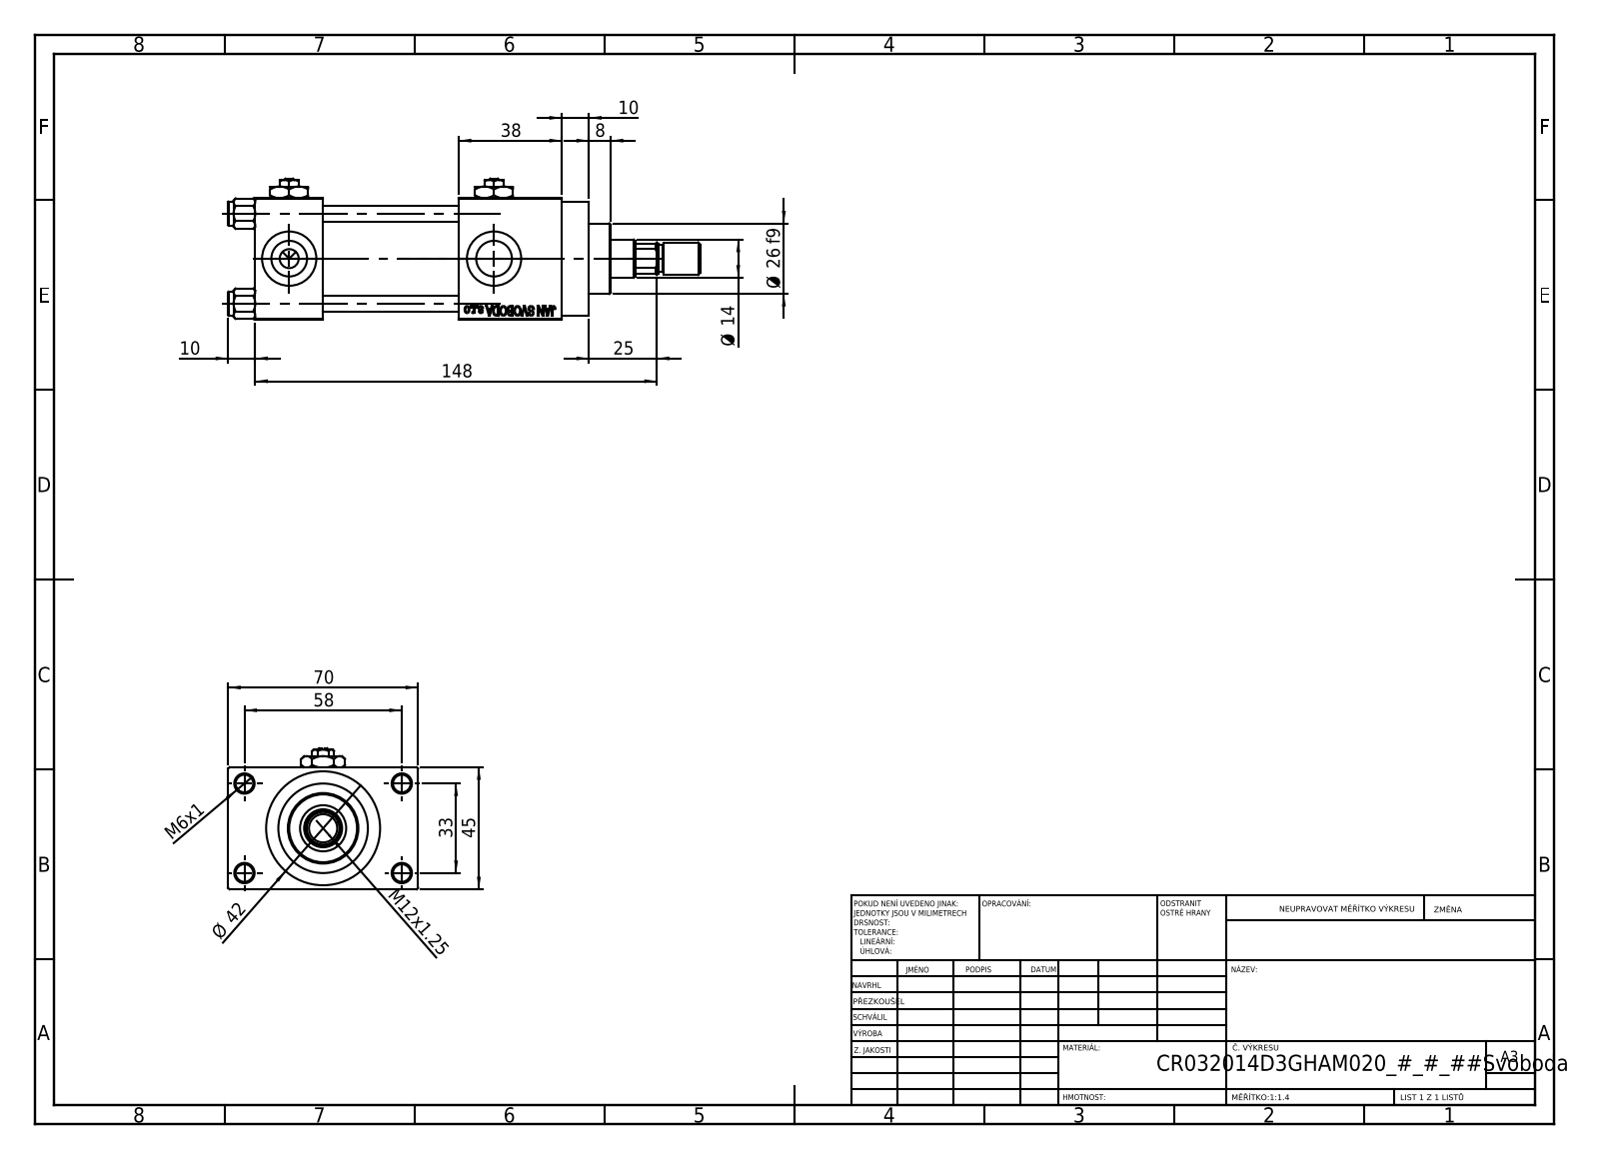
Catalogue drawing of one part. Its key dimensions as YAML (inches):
part_name: "ROD_END_AH; V215CR_D_Body; V215CR_D_TYCINKA; V215CR_VCP_D (+3 more)"
step_written_by: "SolidWorks 2019 (CONFIG_CONTROL_DESIGN)"
units: inches
bodies: {solids: 14, faces: 1215, planar: 546, cylindrical: 103, other: 566}
overall_size: [6.85, 2.756, 2.047]
volume: 14.08
surface_area: 120.9
round_holes:
  - {diameter: 0.256, count: 5}
  - {diameter: 0.236, count: 4}
  - {diameter: 0.518, count: 4}
  - {diameter: 0.787, count: 4}
  - {diameter: 0.276, count: 3}
  - {diameter: 0.551, count: 1}
  - {diameter: 0.669, count: 1}
  - {diameter: 0.945, count: 1}
  - {diameter: 1.26, count: 1}
  - {diameter: 1.299, count: 1}
round_bosses_or_shafts:
  - {diameter: 0.354, count: 4}
  - {diameter: 1.654, count: 1}
  - {diameter: 1.496, count: 1}
  - {diameter: 1.024, count: 1}
  - {diameter: 0.472, count: 1}
  - {diameter: 0.394, count: 1}
partial_cylinders:
  - {radius: 0.256, count: 1}
face_to_face_distances: [1.772, 0.984, 1.969, 0.492, 2.953, 2.264, 3.465, 1.496, 4.449, 2.756]
hole_center_spacings: [0.488, 0.924, 1.307, 1.314, 1.392, 1.795, 2.219, 1.299]
